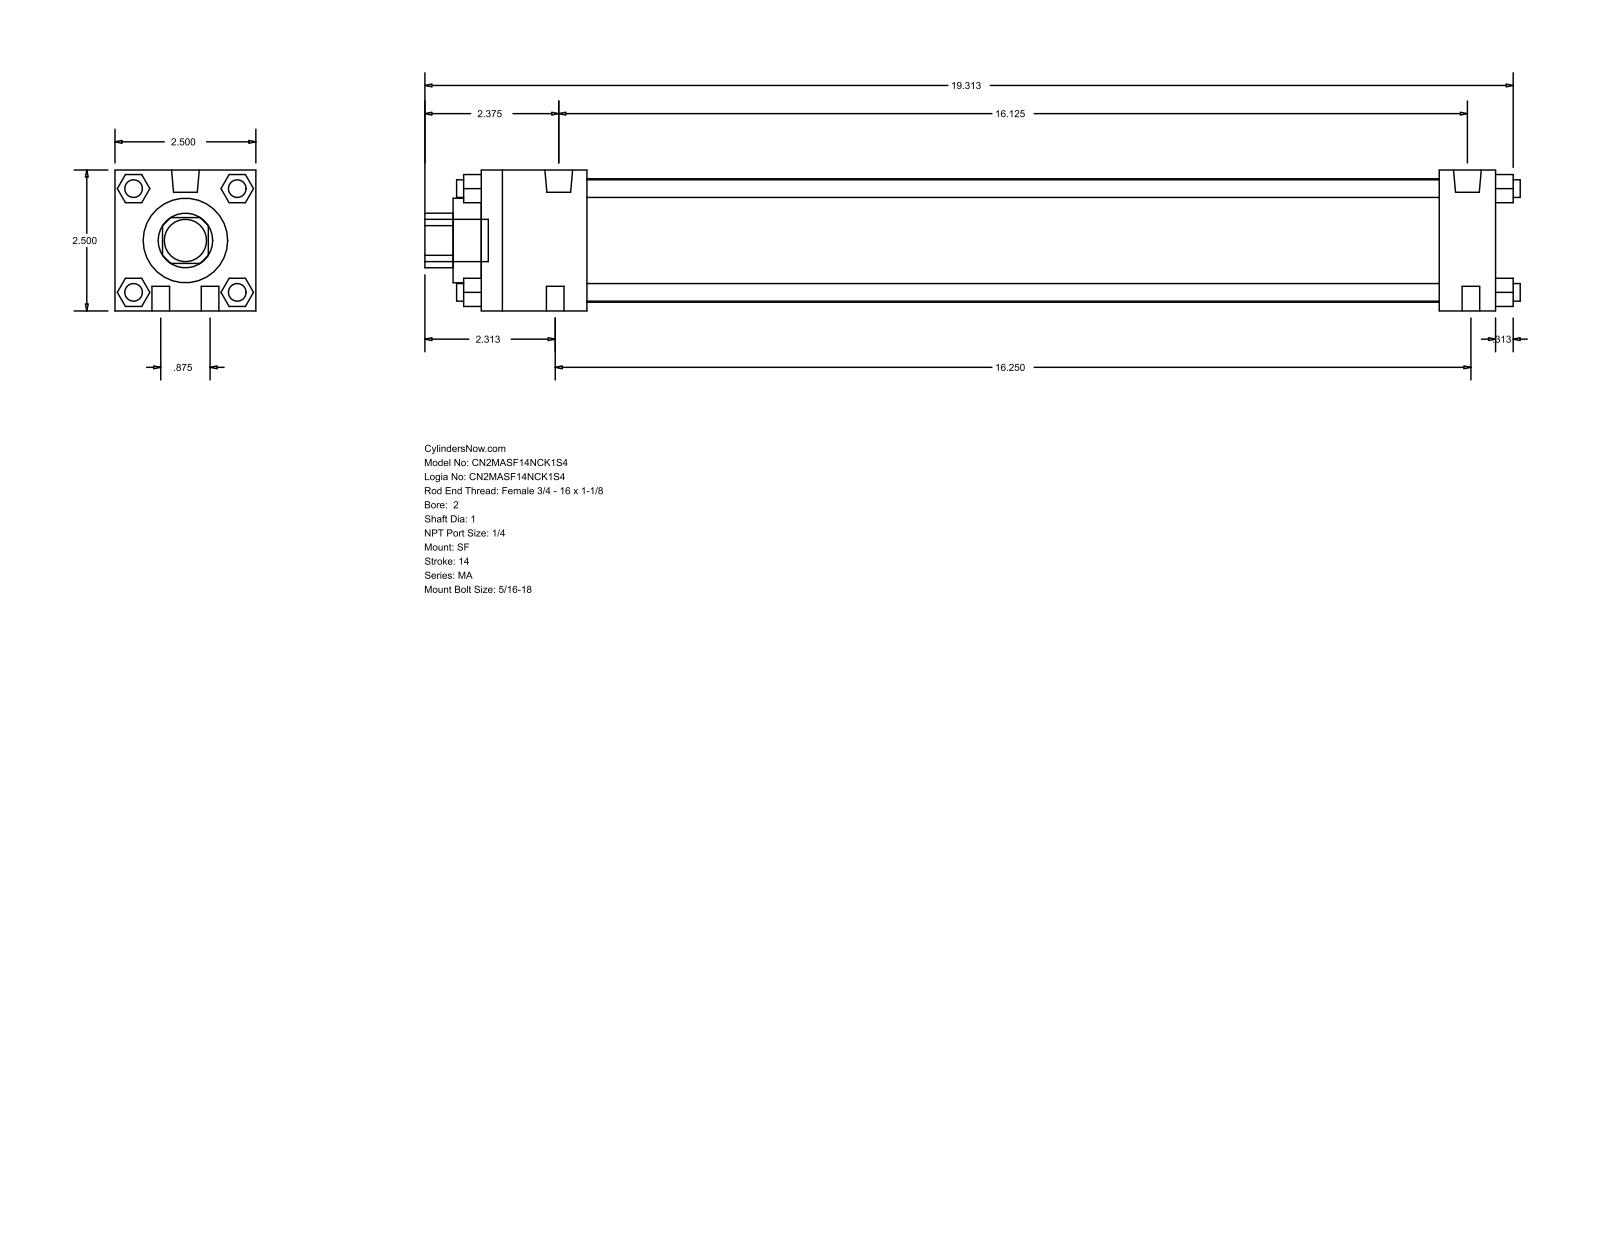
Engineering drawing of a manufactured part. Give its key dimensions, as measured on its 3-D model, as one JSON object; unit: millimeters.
{"part_name": "MA_SF__0200_1", "step_written_by": "GSSL Pune (CONFIG_CONTROL_DESIGN)", "units": "millimeters", "bodies": {"solids": 0, "faces": 124, "planar": 94, "cylindrical": 30, "other": 0}, "overall_size": [493.71, 63.5, 63.5], "round_holes": [[25.4, 1], [38.1, 1], [55.63, 1]], "round_bosses_or_shafts": [[7.94, 10], [12.49, 2], [19.05, 1]], "partial_cylinders_radius": [[12.29, 1]], "face_to_face_distances": [63.5, 457.2, 12.7, 25.4, 431.8, 47.63, 384.17, 409.57, 23.37, 40.47]}
